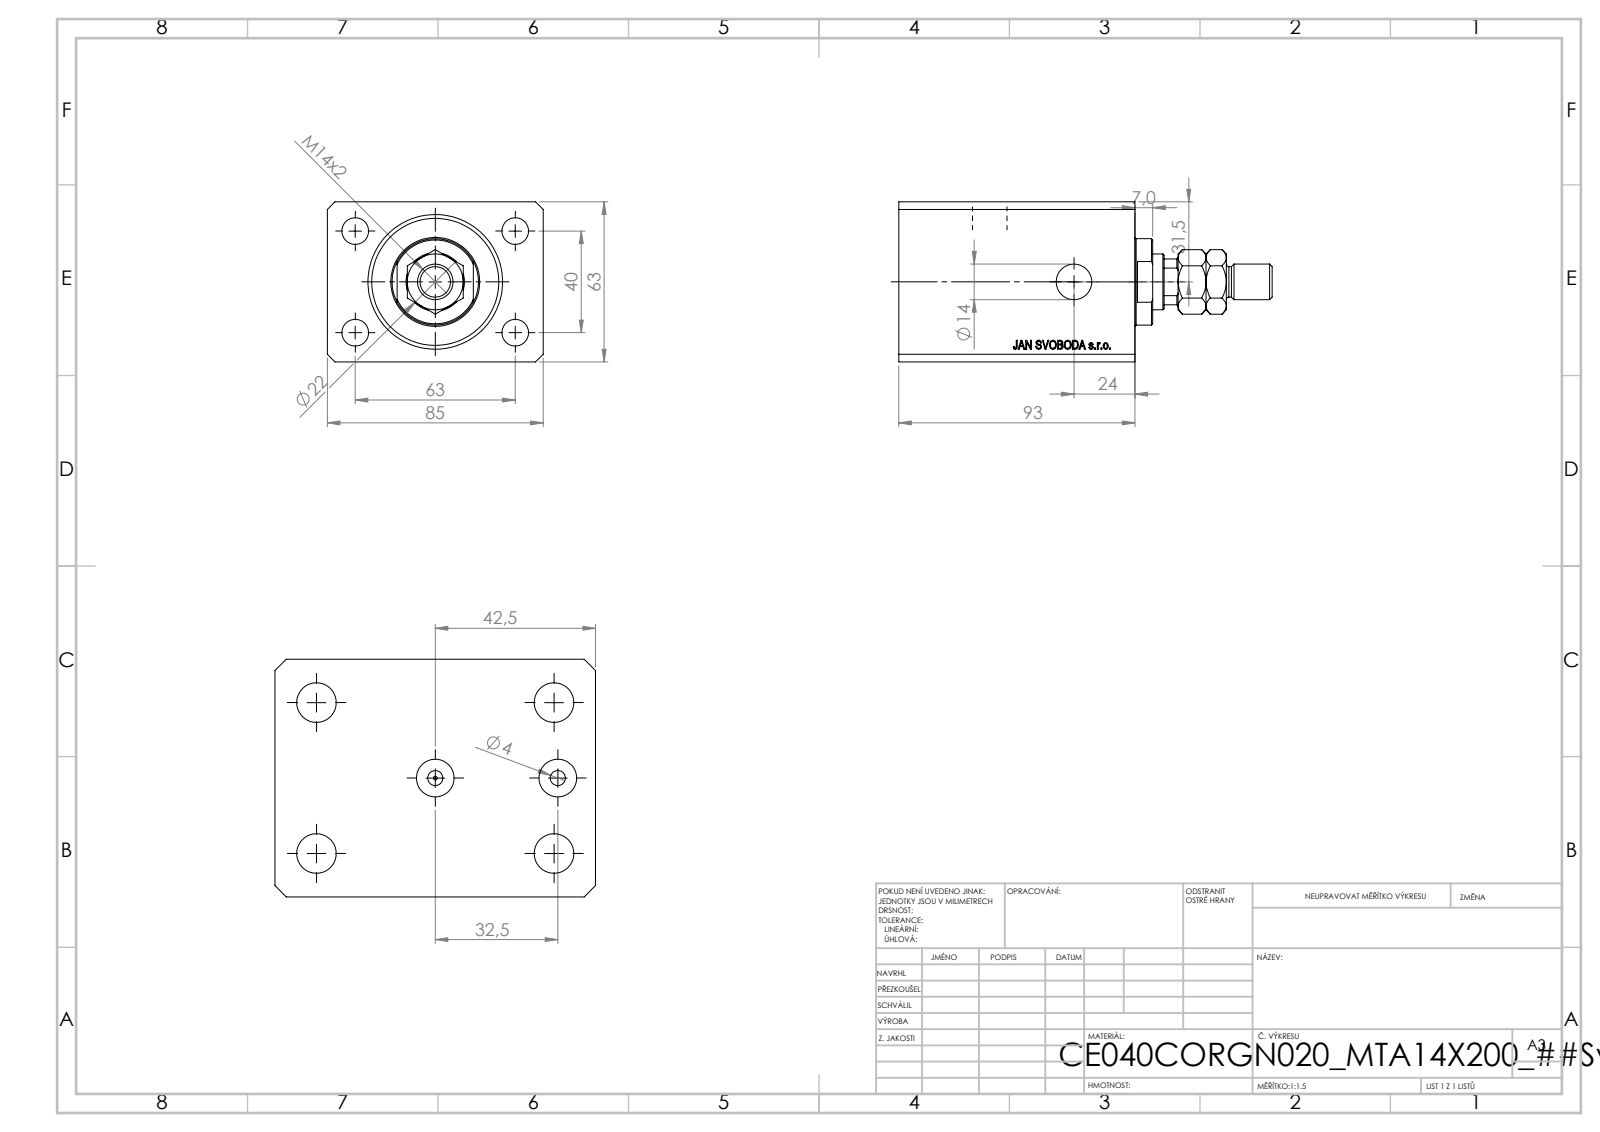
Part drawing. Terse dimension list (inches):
name: V250CE_C_VCP; MTA; V250CE_C_Body; V250CE_VC_C
written by: SolidWorks 2019 (CONFIG_CONTROL_DESIGN)
unit: in
bodies: 4 solids, 915 faces (443 planar, 48 cylindrical, 424 other)
size: 5.787 × 3.346 × 2.48
volume: 28.09 in³; area: 134.8 in²
holes: 4× ⌀0.413, 3× ⌀0.157, 2× ⌀0.394, 2× ⌀0.551, 1× ⌀0.049, 1× ⌀0.492, 1× ⌀0.866, 1× ⌀1.575, 1× ⌀2.087
bosses: 1× ⌀1.339, 1× ⌀0.551, 1× ⌀0.472
rounds: 1× R0.413
face distances: 2.48, 3.346, 3.661, 0.669, 2.992, 0.449, 2.543, 3.213, 0.787, 1.457
hole spacings: 1.469, 0.788, 1.575, 2.48, 2.64, 2.938, 1.28, 1.772
